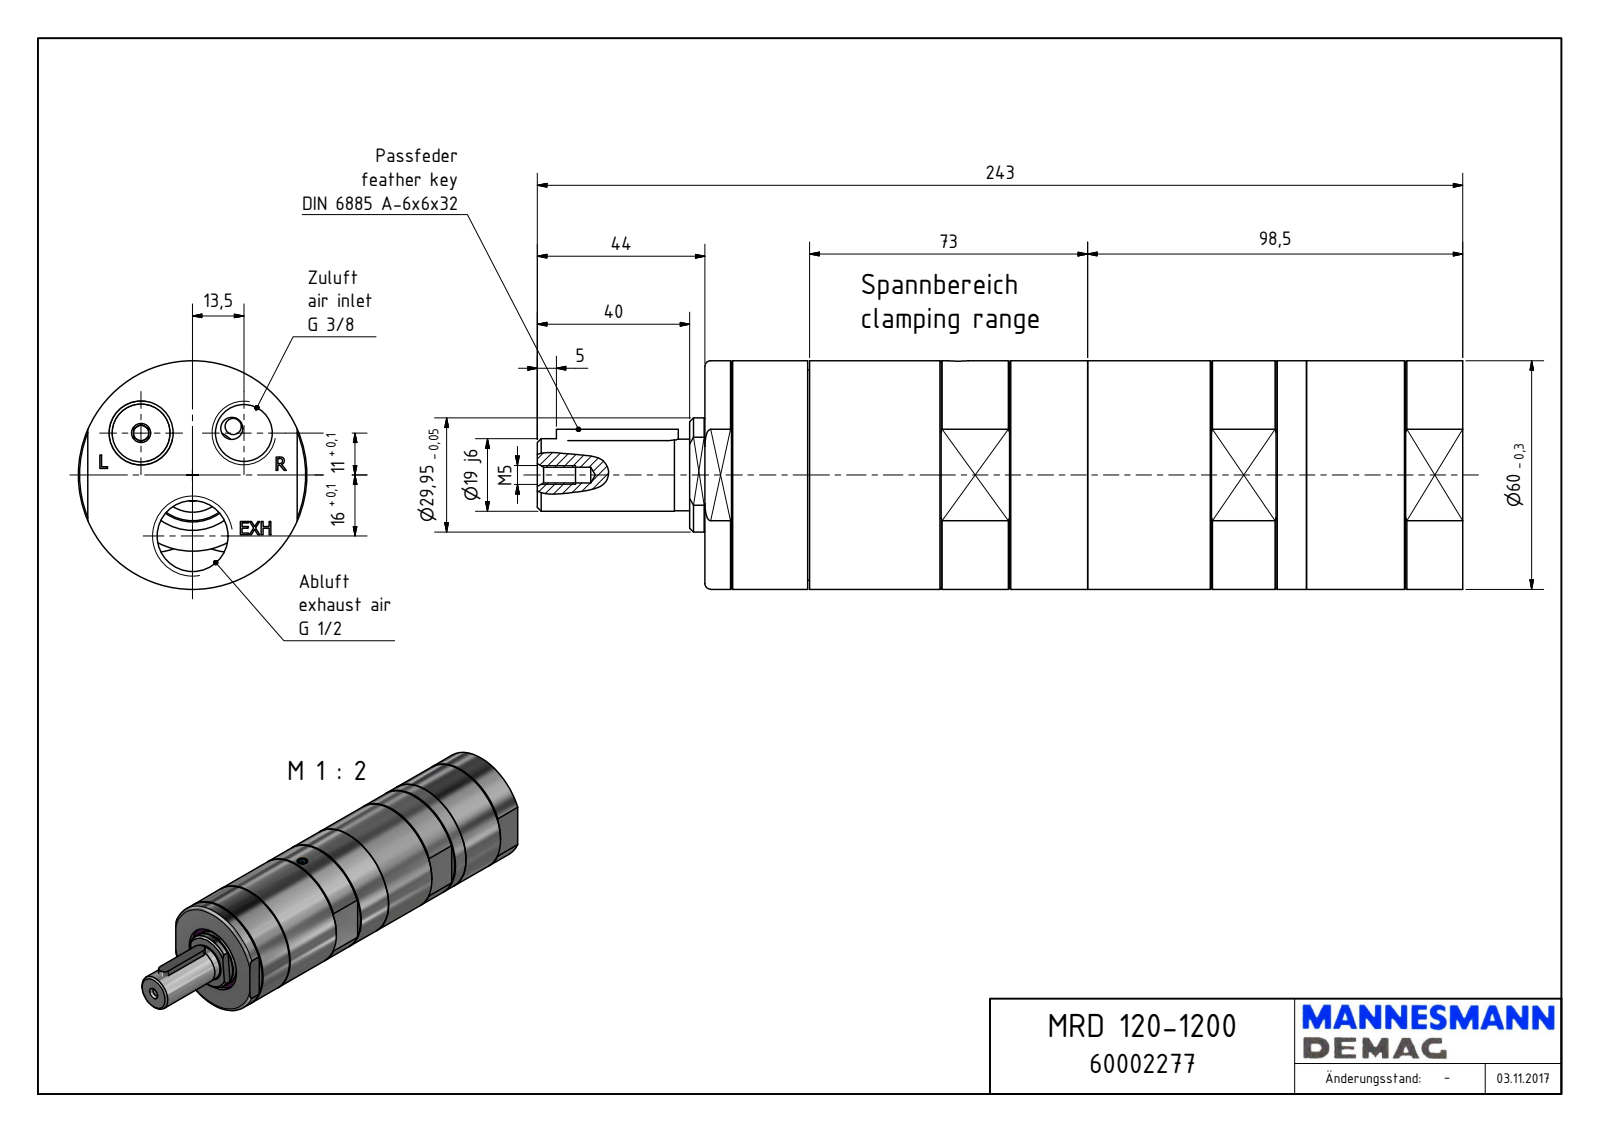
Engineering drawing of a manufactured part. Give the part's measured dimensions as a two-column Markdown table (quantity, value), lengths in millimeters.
| quantity | value |
| --- | --- |
| part name | MRD 120-1200_60002277 |
| STEP written by | Autodesk Inventor 2018 (AUTOMOTIVE_DESIGN) |
| units | millimeters |
| bodies | 1 solid, 227 faces (127 planar, 50 cylindrical, 50 other) |
| overall size | 243 × 60 × 60 |
| volume | 559 305 mm³ |
| surface area | 54 755 mm² |
| round holes (diameter × count) | 4 × 2, 14.95 × 2, 1.55 × 1, 4.13 × 1, 5.5 × 1, 18.63 × 1, 35 × 1, 53.38 × 1, 55.38 × 1, 57 × 1 |
| round bosses / shafts (diameter × count) | 60 × 1, 55.18 × 1, 54.38 × 1, 53.18 × 1, 29.95 × 1, 19 × 1, 18.8 × 1, 5 × 1 |
| partial cylindrical surfaces (radius × count) | 3 × 2, 7.5 × 2, 8.5 × 1, 19.5 × 1, 23.5 × 1, 25.37 × 1 |
| main face-to-face distances | 199, 55, 182.56, 16.44, 186, 3.44, 13, 27.5, 155.06, 158.5 |
| hole center spacings | 17.41, 30.19, 16, 27 |
